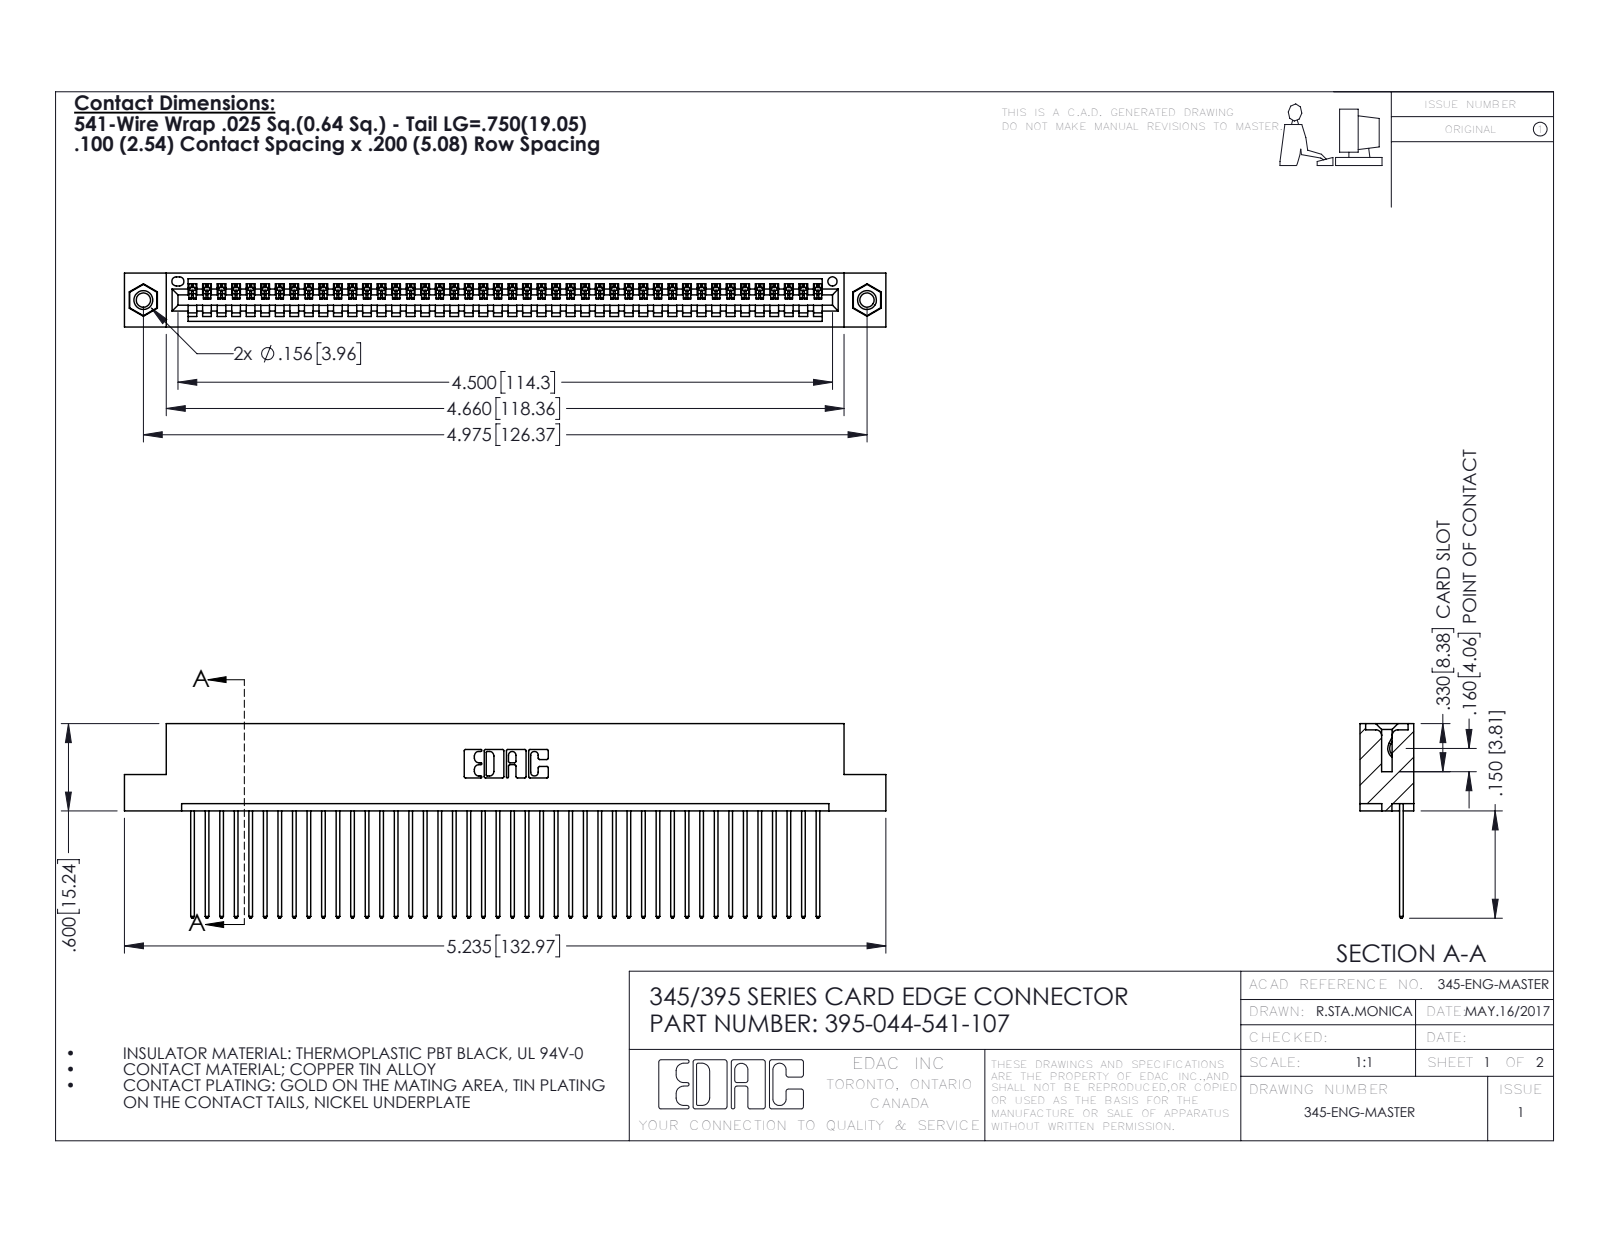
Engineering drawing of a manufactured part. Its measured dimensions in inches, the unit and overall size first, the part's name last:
Units: inches
Overall size (bounding box): 5.235 × 1.337 × 0.37
Round holes (diameter × count): ⌀0.098 ×2, ⌀0.125 ×2, ⌀0.156 ×2, ⌀0.064 ×1
Round bosses / shafts (diameter × count): ⌀0.155 ×2
Partial cylindrical surfaces — rounded edges, fillets, slot ends (radius × count): R0.006 ×88, R0.01 ×88, R0.01 ×22, R0.007 ×6, R0.031 ×6, R0.026 ×3, R0.031 ×2, R0.04 ×2
Main face-to-face distances: 0.072, 0.298, 0.098, 0.272, 0.025, 0.37, 0.2, 0.225, 0.149, 0.072
Hole centre spacings: 0.27, 4.739, 4.975
Volume: 0.78 in³ · Surface area: 27.74 in²
Bodies: 47 solids, 2738 faces (1872 planar, 850 cylindrical, 16 other)
Part name (STEP PRODUCT): 345-292-001_345-293-141; 345-250-001_345-250-005-103; 345 Part_Flush Mounting Lugs - 0.156 Dia-TI; 395-044-541-107
STEP written by: SolidWorks 2016 (CONFIG_CONTROL_DESIGN)
